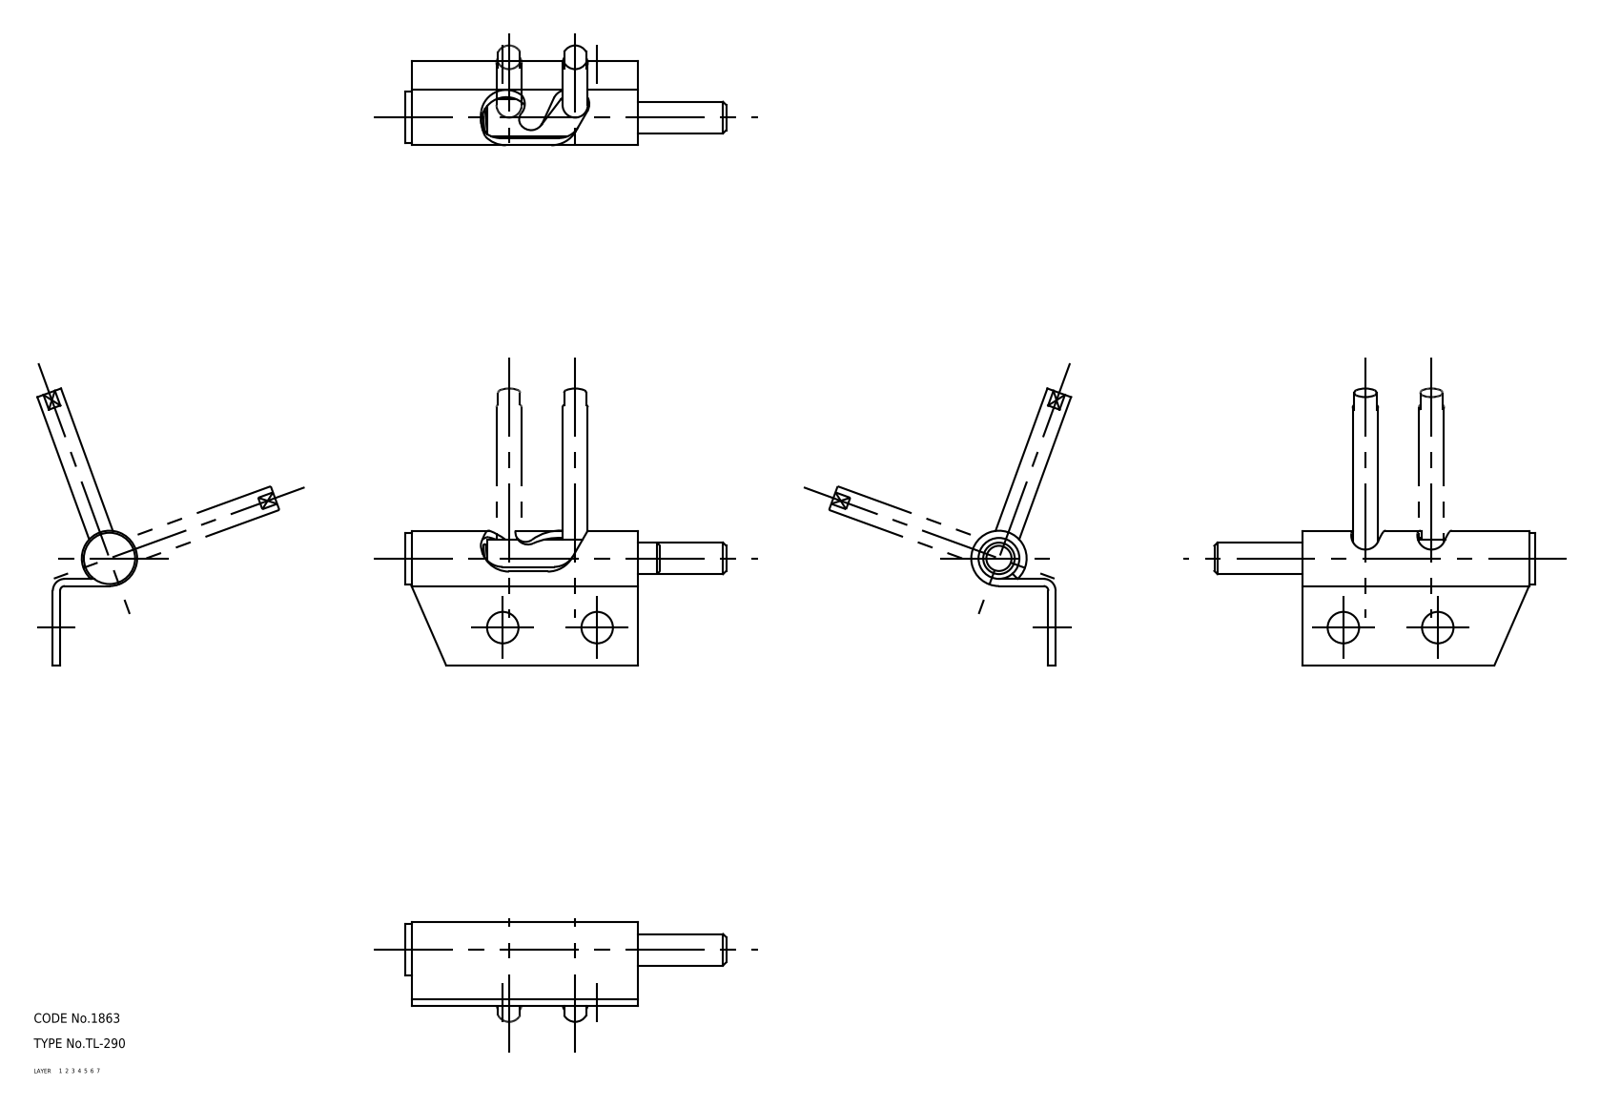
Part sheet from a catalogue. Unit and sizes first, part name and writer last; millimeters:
Units: millimetres
Overall size (bounding box): 102 × 87.82 × 31.54
Volume: 22 708 mm³ · Surface area: 16 516 mm²
Bodies: 4 solids, 58 faces (0 planar, 0 cylindrical, 58 other)
Part name (STEP PRODUCT): latch; knob; housing_B; housing_A (+1 more)
STEP written by: CADfix (AUTOMOTIVE_DESIGN)
